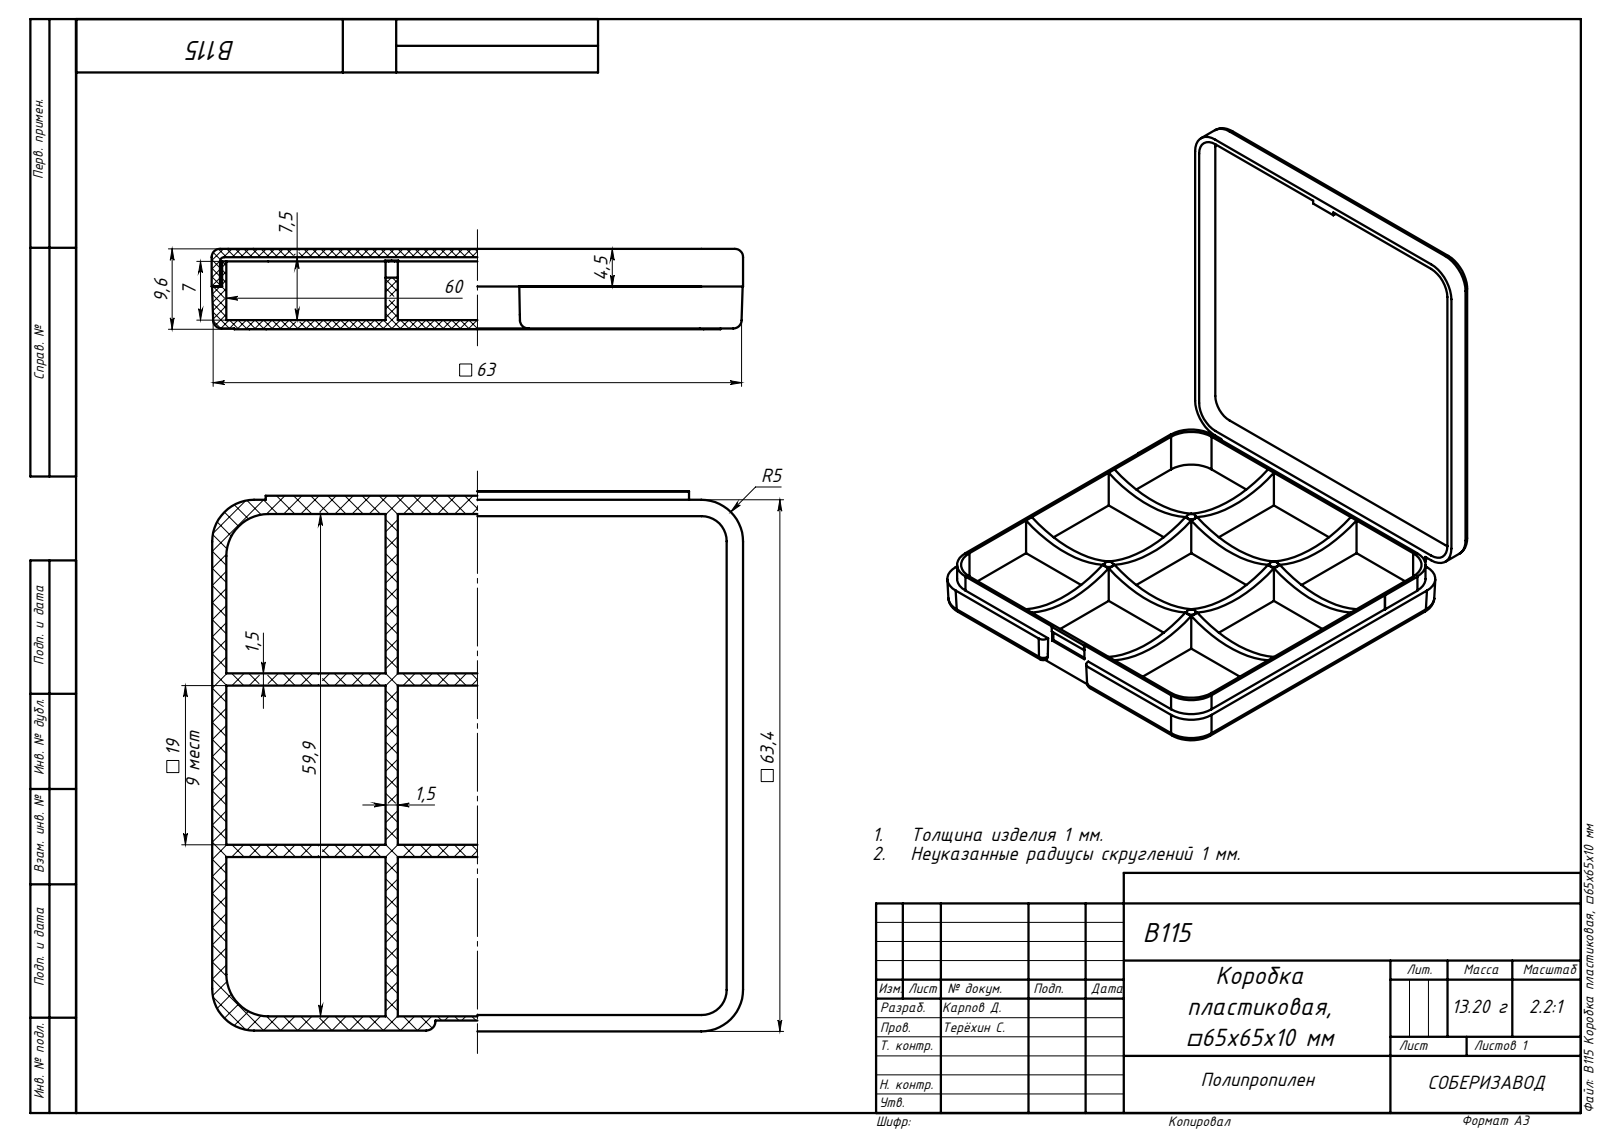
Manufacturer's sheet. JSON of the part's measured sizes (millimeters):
{"part_name": "B115 Емкость; B115 Коробка пластиковая, ?65x65x10 мм; B115 Крышка", "step_written_by": "SolidWorks 2020 (AUTOMOTIVE_DESIGN)", "units": "millimeters", "bodies": {"solids": 2, "faces": 231, "planar": 145, "cylindrical": 67, "other": 19}, "overall_size": [64.41, 63.41, 9.6], "volume_mm3": 12281, "surface_area_mm2": 23902, "round_bosses_or_shafts": [[1.6, 4]], "partial_cylinders_radius": [[5, 16], [1, 8], [2, 8], [23.56, 6], [0.5, 4], [3, 4], [4, 4], [1.1, 2]], "face_to_face_distances": [1, 8.5, 0.9, 9.4, 7.5, 8.4, 20.45, 19, 1.45, 39.45]}
